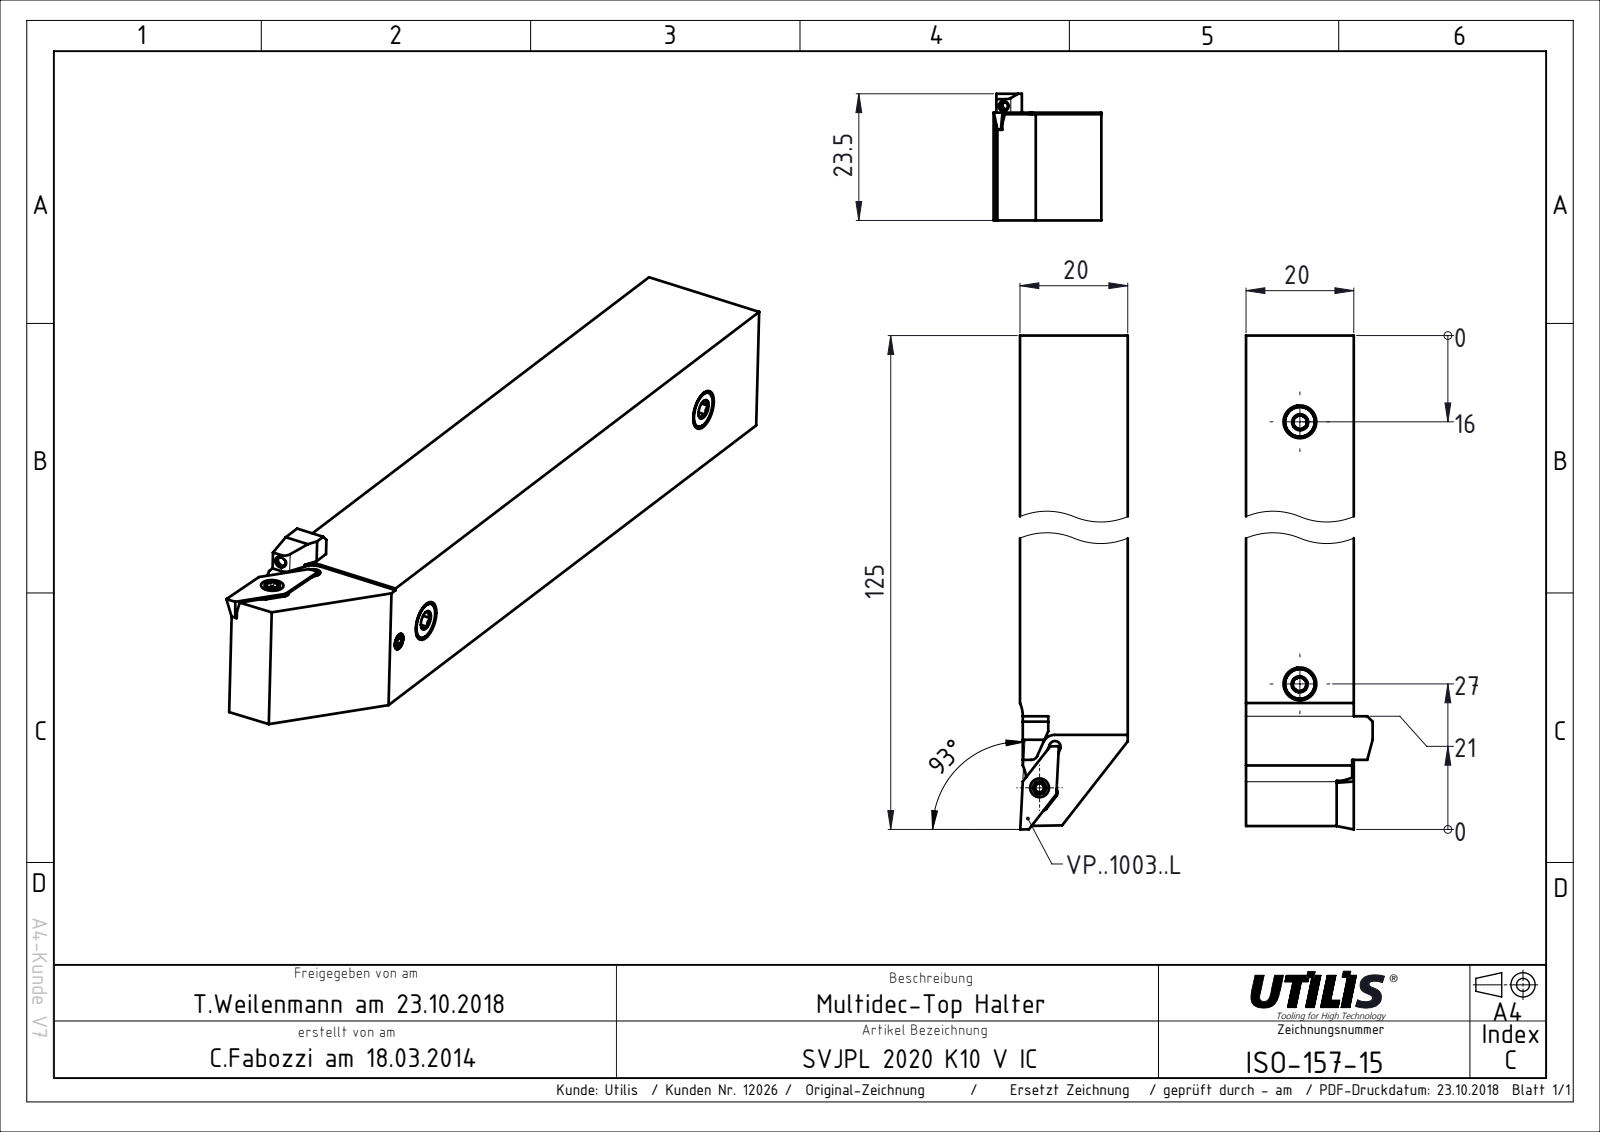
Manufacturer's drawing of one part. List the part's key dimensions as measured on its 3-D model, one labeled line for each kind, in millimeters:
Part name (STEP PRODUCT): ISO-157-15
STEP written by: SolidWorks 2016 (AUTOMOTIVE_DESIGN)
Units: millimetres
Bodies: 1 solid, 49 faces (42 planar, 7 cylindrical, 0 other)
Overall size (bounding box): 125 × 23.5 × 20.2
Volume: 47 607 mm³ · Surface area: 10 555 mm²
Partial cylindrical surfaces — rounded edges, fillets, slot ends (radius × count): R1.05 ×3, R6.1 ×2, R2.3 ×1
Main face-to-face distances: 20, 19.73, 19.7, 23.5, 3.8, 3.5, 16.82, 2.88, 3.18, 6.68
